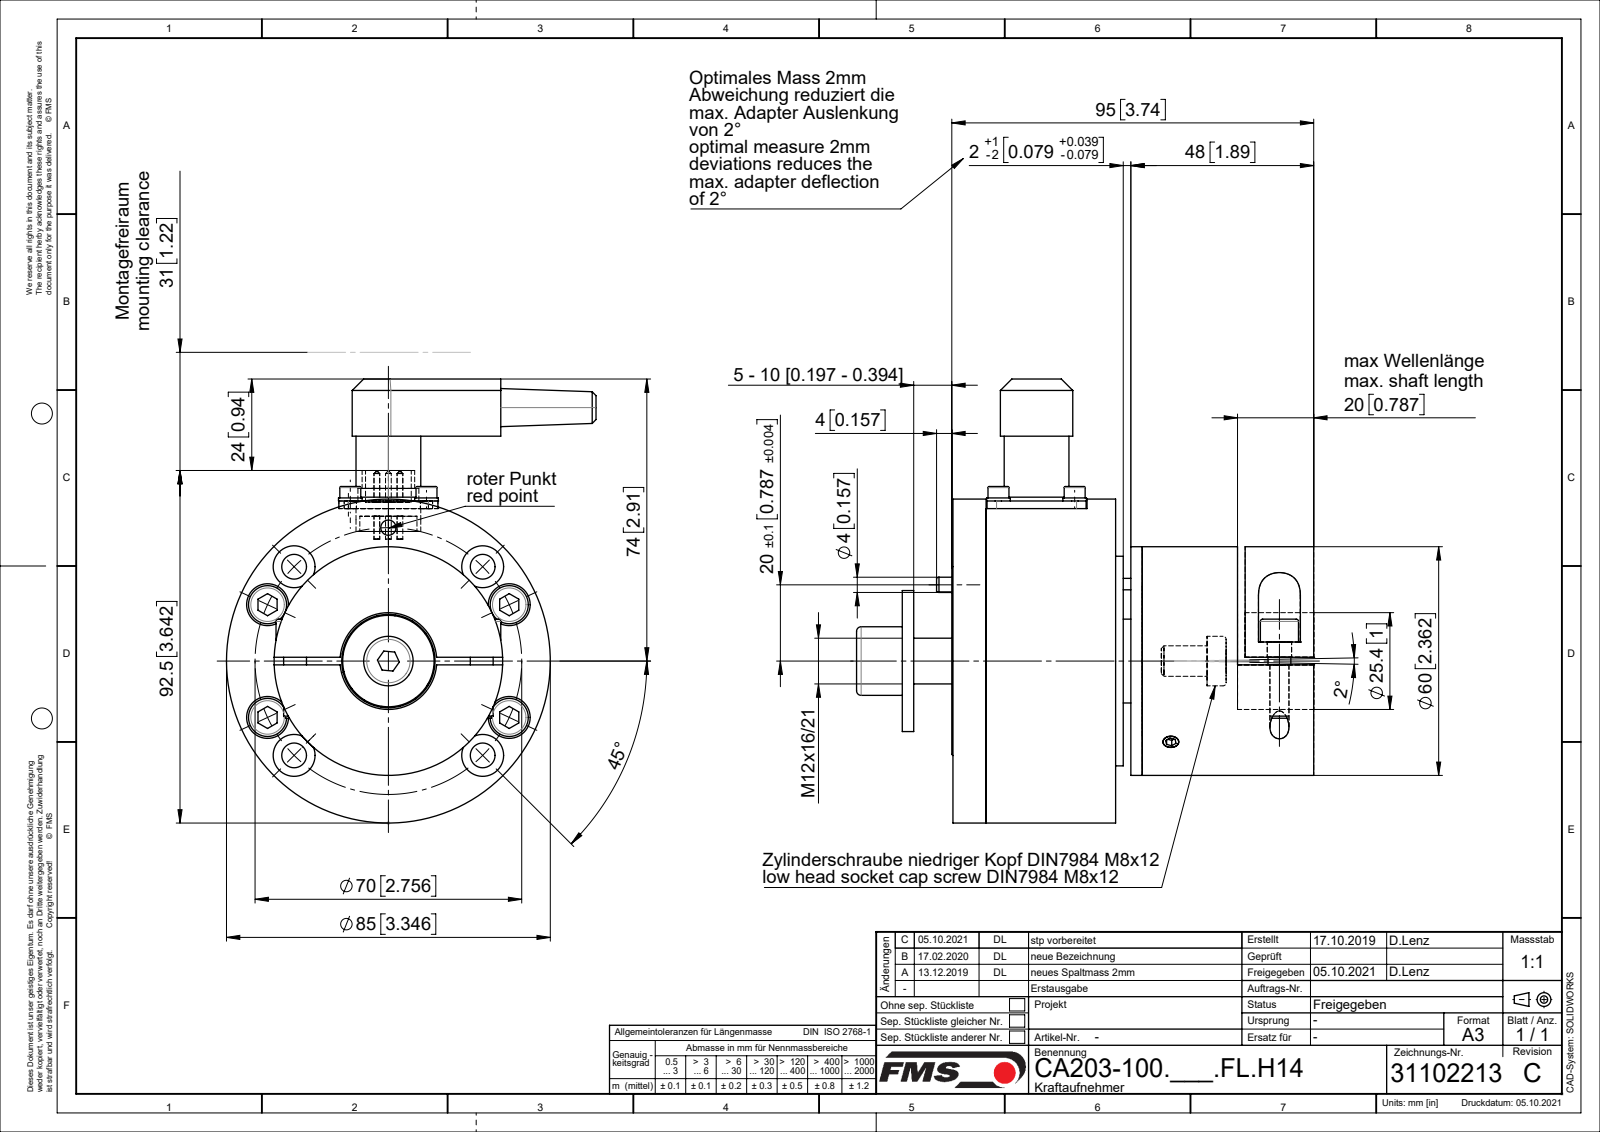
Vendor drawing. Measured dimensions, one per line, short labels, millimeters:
name: Sch DIN9021_M12; Spannstift_ISO13337_D04x10; Zyl-Schr DIN912_M6x20; RKL_6203_01 (+8 more)
written by: SolidWorks 2018 (CONFIG_CONTROL_DESIGN)
unit: mm
bodies: 43 solids, 803 faces (278 planar, 333 cylindrical, 192 other)
size: 120 × 116.5 × 97
volume: 314 985 mm³; area: 113 810 mm²
holes: 8× ⌀2.5, 8× ⌀6.5, 8× ⌀11, 6× ⌀5, 5× ⌀2, 5× ⌀4, 4× ⌀3.1, 4× ⌀3.2, 4× ⌀3.6, 4× ⌀7, 2× ⌀3, 2× ⌀6.4
bosses: 8× ⌀3, 7× ⌀6, 6× ⌀10, 5× ⌀1.5, 4× ⌀6.2, 4× ⌀5.7, 4× ⌀5.5, 1× ⌀85
rounds: 4× R2.5, 2× R5, 2× R5.5, 1× R9.5
face distances: 2, 45, 41, 10, 30, 3, 60, 34, 50, 22
hole spacings: 35, 20, 24.78, 25.2, 32.8, 51.14, 56.46, 6
